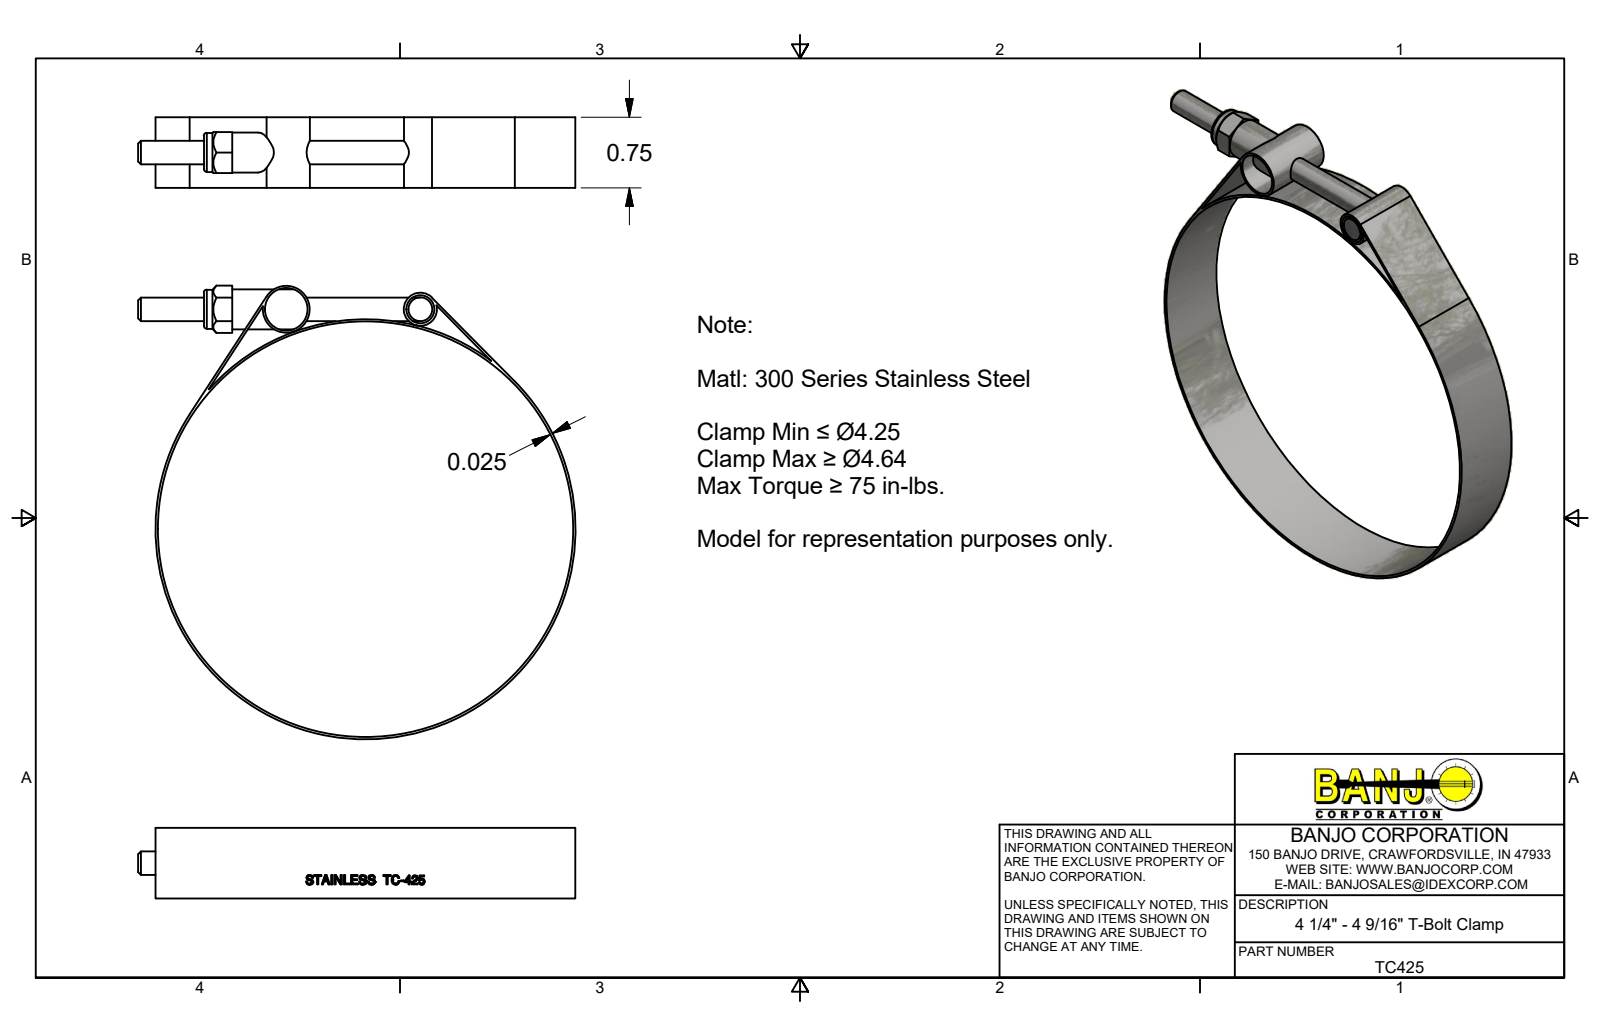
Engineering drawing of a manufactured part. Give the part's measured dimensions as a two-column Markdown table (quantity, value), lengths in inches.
| quantity | value |
| --- | --- |
| part name | TC425 |
| STEP written by | Autodesk Inventor 2018 (AUTOMOTIVE_DESIGN) |
| units | inches |
| bodies | 1 solid, 230 faces (101 planar, 36 cylindrical, 93 other) |
| overall size | 4.814 × 4.646 × 0.75 |
| volume | 0.618 in³ |
| surface area | 30.93 in² |
| round holes (diameter × count) | 0.3 × 1, 0.45 × 1, 4.41 × 1 |
| round bosses / shafts (diameter × count) | 0.25 × 2, 4.46 × 1, 0.5 × 1, 0.425 × 1, 0.415 × 1, 0.35 × 1 |
| partial cylindrical surfaces (radius × count) | 2.225 × 1 |
| main face-to-face distances | 0.025, 0.026, 0.75, 0.157, 0.592, 0.435, 0.435, 0.7, 1, 0.3 |
| hole center spacings | 1.425, 2.405, 2.48 |
